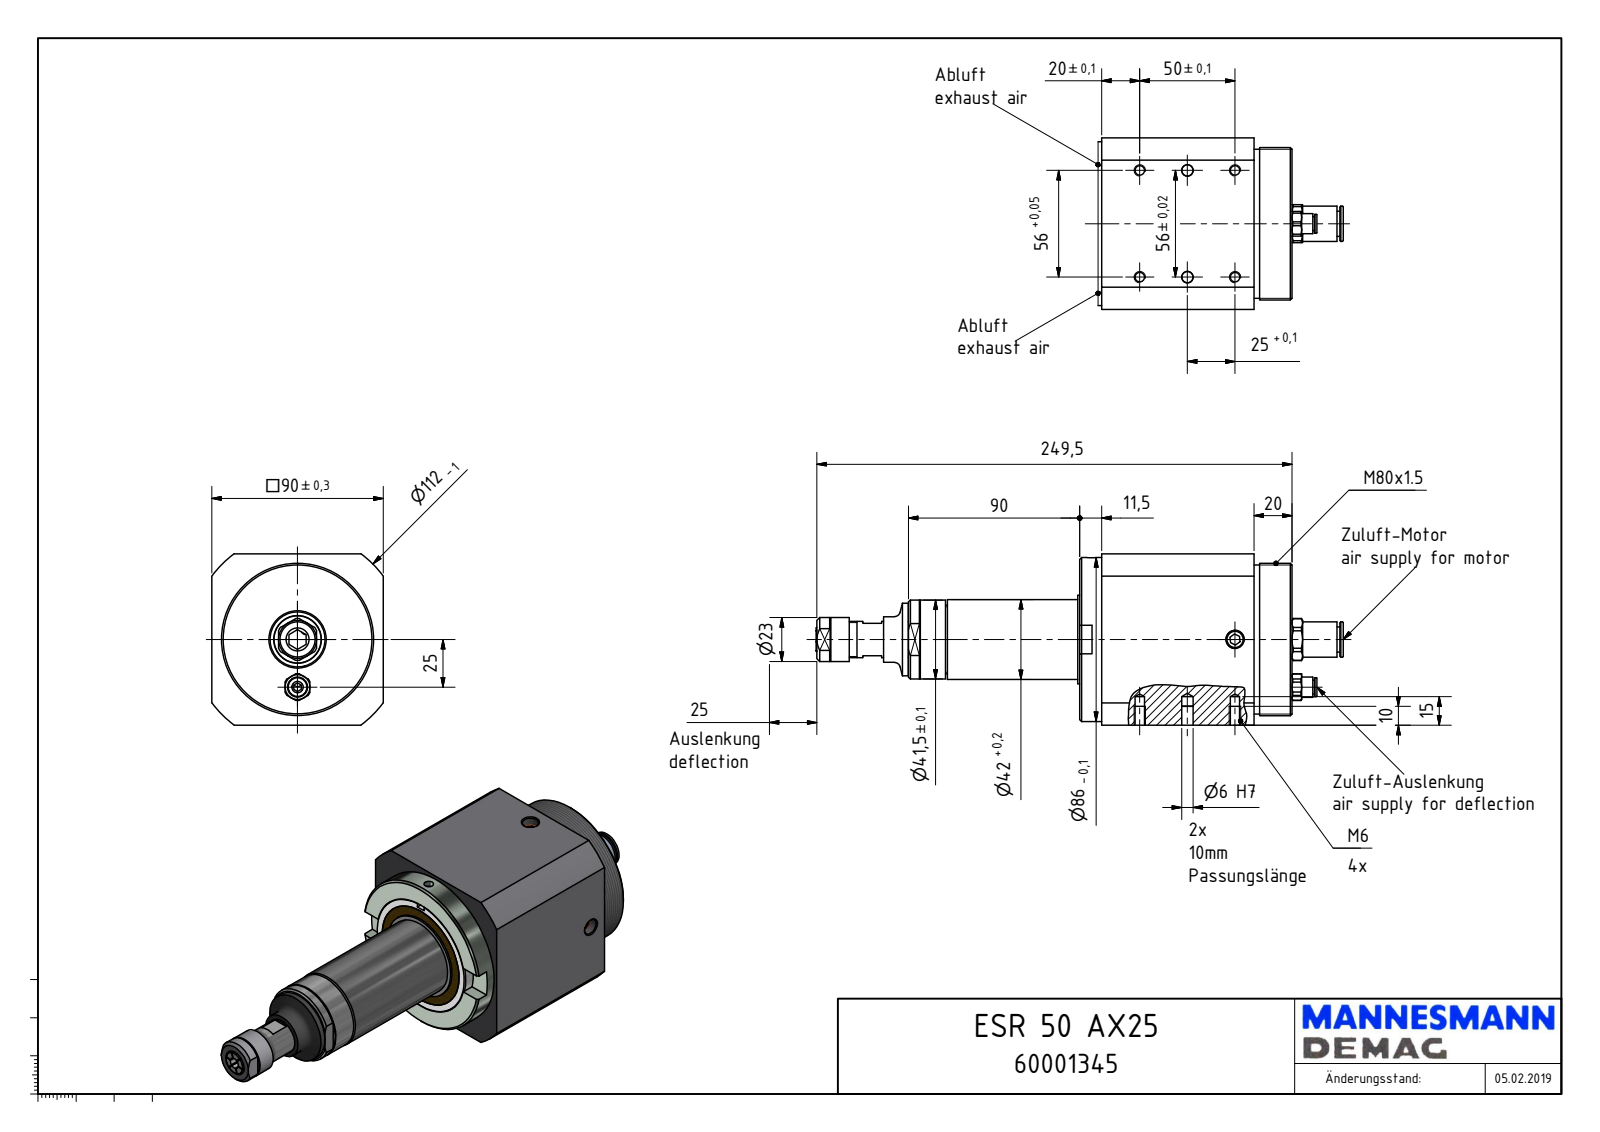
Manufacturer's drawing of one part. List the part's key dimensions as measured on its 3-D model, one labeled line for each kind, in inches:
Part name (STEP PRODUCT): ESR 50 AX25_60001345
STEP written by: Autodesk Inventor 2018 (AUTOMOTIVE_DESIGN)
Units: inches
Bodies: 1 solid, 313 faces (146 planar, 85 cylindrical, 82 other)
Overall size (bounding box): 10.898 × 3.543 × 3.543
Volume: 57.32 in³ · Surface area: 117.3 in²
Round holes (diameter × count): ⌀0.194 ×4, ⌀0.236 ×4, ⌀0.337 ×3, ⌀0.236 ×2, ⌀0.197 ×1, ⌀0.472 ×1, ⌀0.52 ×1, ⌀0.768 ×1, ⌀0.984 ×1, ⌀1.181 ×1, ⌀2.559 ×1
Round bosses / shafts (diameter × count): ⌀3.386 ×1, ⌀3.15 ×1, ⌀3.078 ×1, ⌀1.831 ×1, ⌀1.654 ×1, ⌀1.634 ×1, ⌀1.496 ×1, ⌀1.417 ×1
Partial cylindrical surfaces — rounded edges, fillets, slot ends (radius × count): R1.328 ×6, R0.276 ×1, R0.433 ×1, R1.531 ×1, R1.61 ×1, R2.205 ×1
Main face-to-face distances: 3.543, 4.39, 0.787, 3.602, 0.453, 3.15, 3.937, 3.996, 7.146, 7.933
Hole centre spacings: 0.984, 2.415, 2.205, 1.102, 1.478, 1.491, 1.969, 2.256
